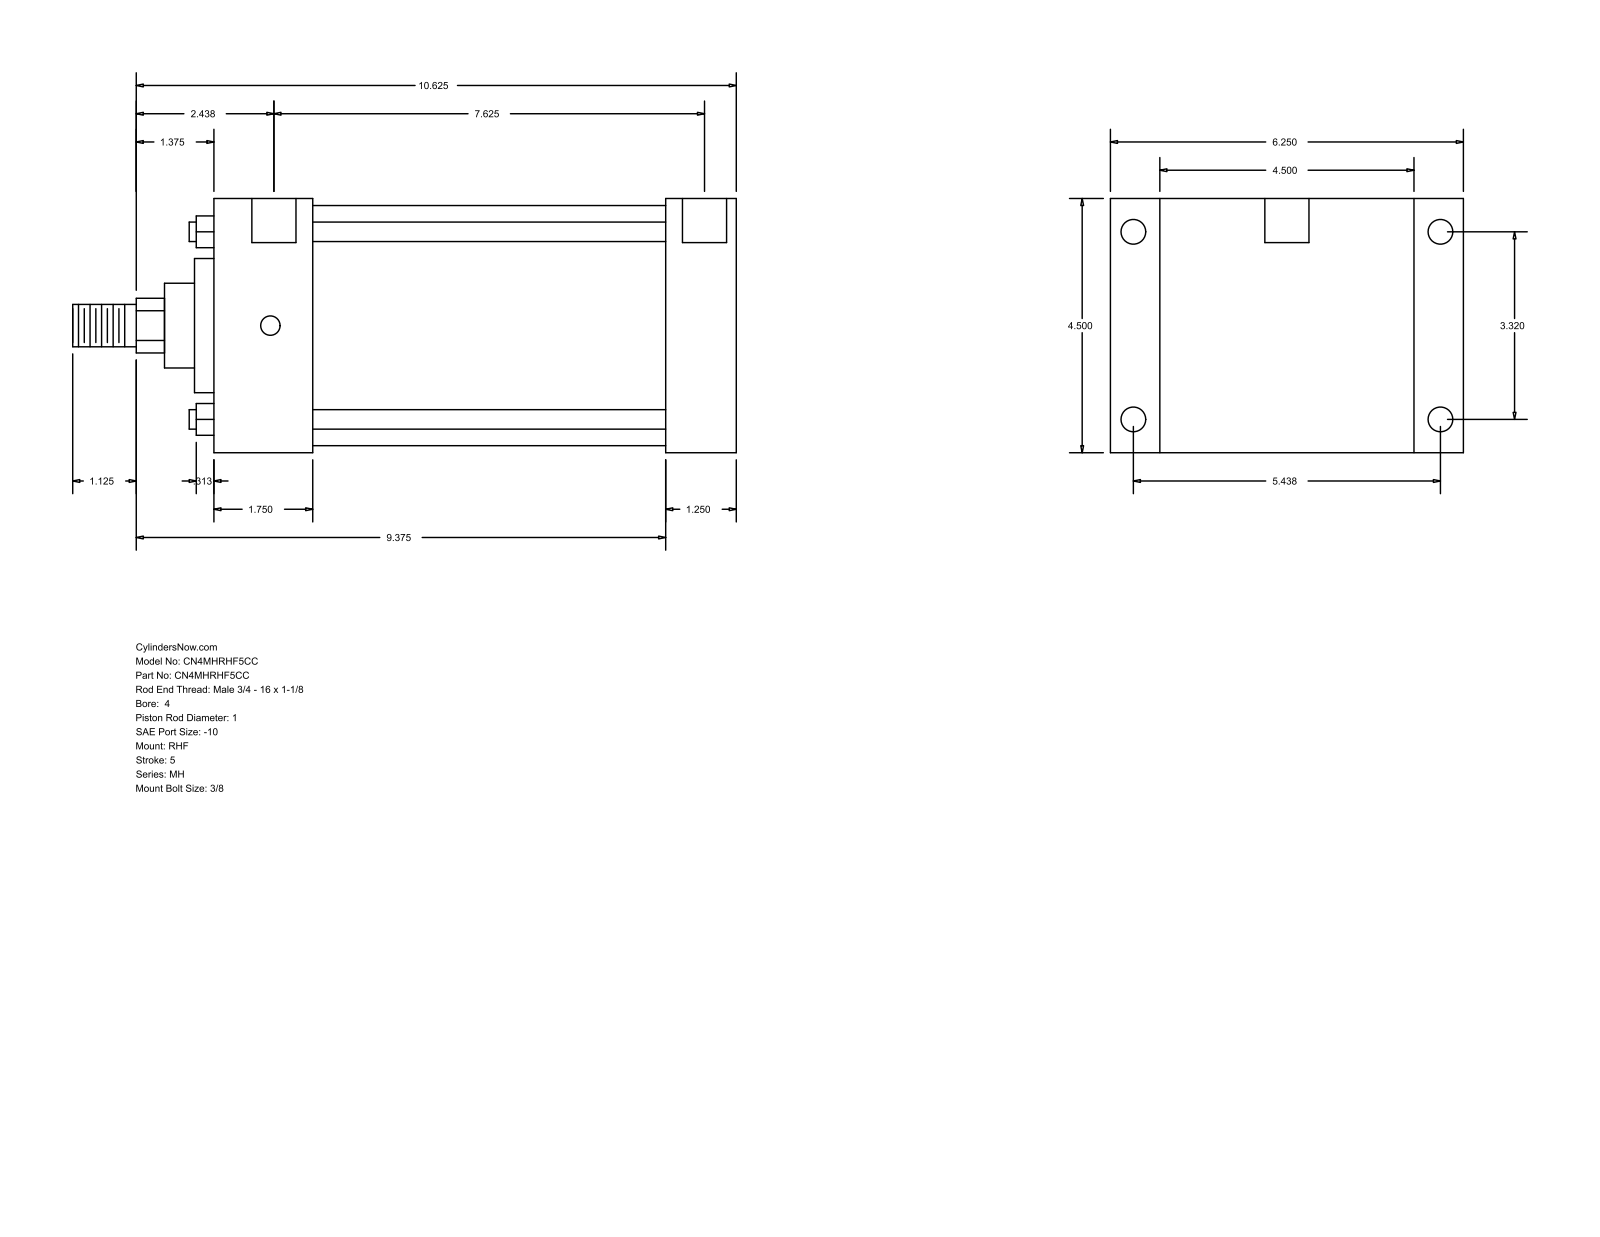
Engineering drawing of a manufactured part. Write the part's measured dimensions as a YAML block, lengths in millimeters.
part_name: "MH_RHF__0400_1"
step_written_by: "GSSL Pune (CONFIG_CONTROL_DESIGN)"
units: millimeters
bodies: {solids: 0, faces: 90, planar: 61, cylindrical: 29, other: 0}
overall_size: [298.45, 158.75, 114.3]
round_holes:
  - {diameter: 8.73, count: 4}
  - {diameter: 11.13, count: 4}
  - {diameter: 19.84, count: 2}
round_bosses_or_shafts:
  - {diameter: 8.76, count: 4}
  - {diameter: 107.95, count: 1}
  - {diameter: 60.33, count: 1}
  - {diameter: 38.1, count: 1}
  - {diameter: 25.4, count: 1}
  - {diameter: 19.05, count: 1}
partial_cylinders:
  - {radius: 12.29, count: 1}
face_to_face_distances: [114.3, 234.96, 203.2, 31.76, 22.23, 136.53, 44.46, 158.74, 190.5, 158.76]
hole_center_spacings: [84.32, 138.12, 161.82, 196.85, 1.58, 1.59, 193.68, 195.26]
